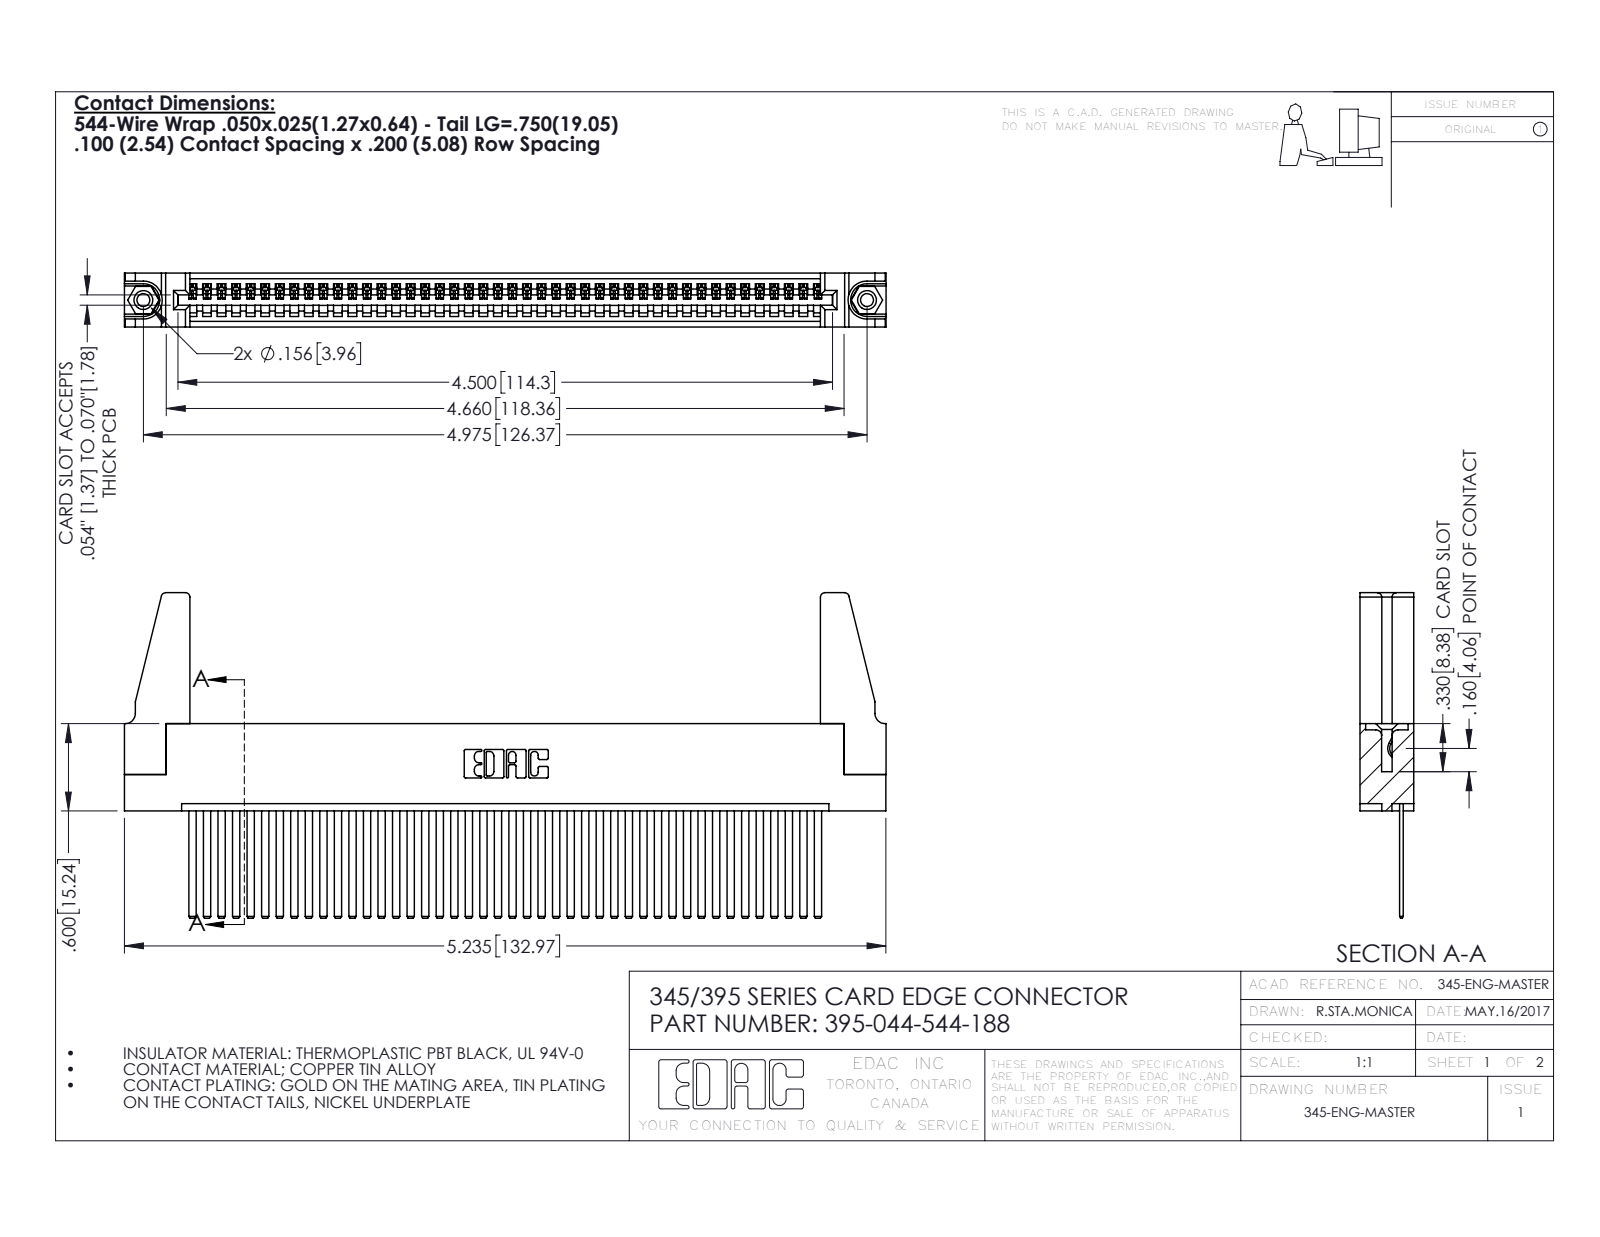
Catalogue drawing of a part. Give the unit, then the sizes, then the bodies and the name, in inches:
Units: inches
Overall size (bounding box): 5.236 × 2.237 × 0.37
Round holes (diameter × count): ⌀0.089 ×2, ⌀0.125 ×2, ⌀0.156 ×2, ⌀0.064 ×1
Round bosses / shafts (diameter × count): ⌀0.155 ×2
Partial cylindrical surfaces — rounded edges, fillets, slot ends (radius × count): R0.006 ×88, R0.01 ×22, R0.03 ×8, R0.007 ×6, R0.031 ×6, R0.026 ×3, R0.031 ×2, R0.04 ×2
Main face-to-face distances: 0.072, 0.298, 0.098, 0.272, 0.025, 0.37, 0.2, 0.225, 0.149, 0.072
Hole centre spacings: 0.27, 4.739, 4.975
Volume: 1.001 in³ · Surface area: 34.37 in²
Bodies: 49 solids, 2538 faces (1736 planar, 786 cylindrical, 16 other)
Part name (STEP PRODUCT): 395-044-544-188; 345-220-078_345-220-088; 345-292-001_345-293-144; 345-250-001_345-250-001-102 (+1 more)
STEP written by: SolidWorks 2016 (CONFIG_CONTROL_DESIGN)
